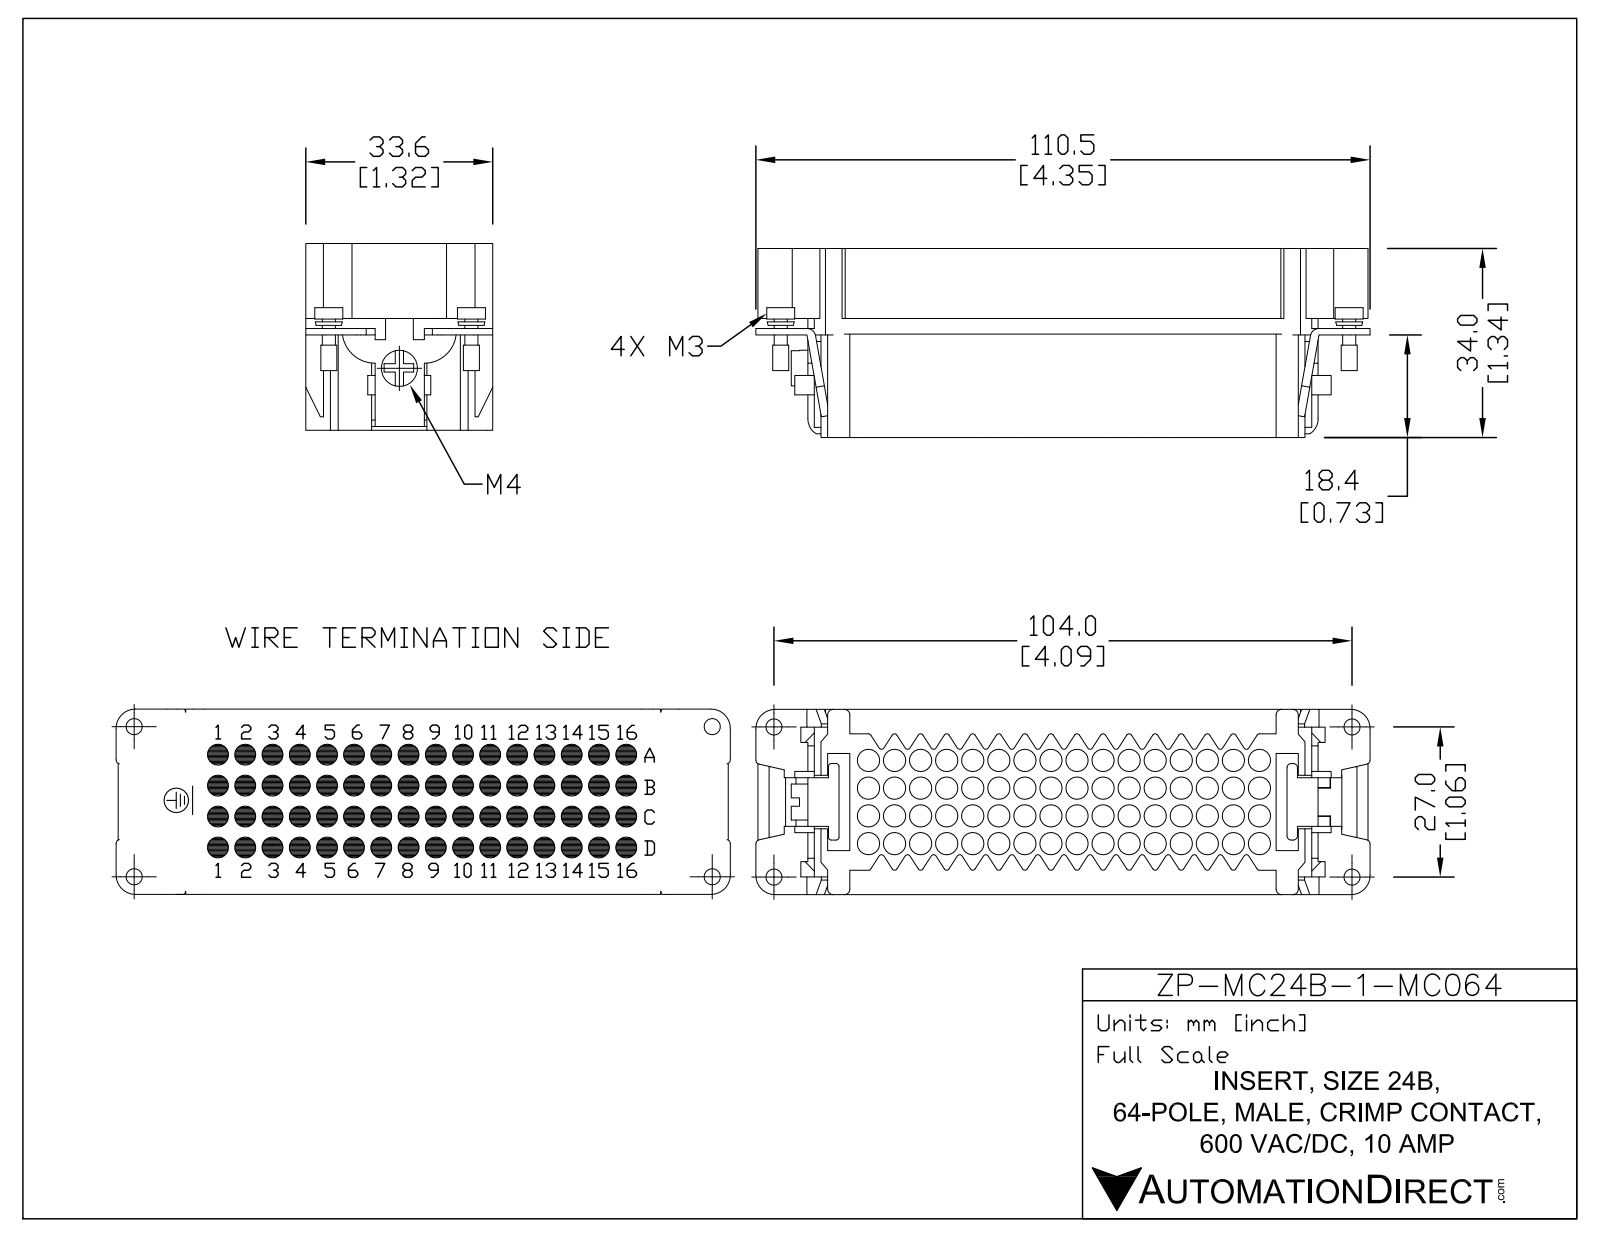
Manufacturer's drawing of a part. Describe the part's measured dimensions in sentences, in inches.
The part is named "ZP-24B-64-MC-INSERT". Its 3-D file was written by "SolidWorks 2011 (AUTOMOTIVE_DESIGN)". It is 2 solids with 613 faces: 377 planar, 232 cylindrical and 4 other. Overall it measures 4.36 by 1.325 by 1.315 inches. Its volume is 2.097 cubic inches and its surface area 67.43 square inches. Round holes: 64 of diameter 0.157, 1 of diameter 0.118. Round bosses or shafts: 32 of diameter 0.187, 4 of diameter 0.199, 4 of diameter 0.114, 4 of diameter 0.093, 1 of diameter 0.256. Partial cylindrical surfaces (rounded edges, fillets, slot ends): 66 of radius 0.02, 16 of radius 0.03, 8 of radius 0.039, 6 of radius 0.059, 4 of radius 0.061, 4 of radius 0.138, 4 of radius 0.258, 2 of radius 0.226. The main face-to-face distances are 0.069, 1.148, 0.156, 0.777, 1.217, 1.079, 0.793, 0.045, 0.048, 0.049. The hole center spacings are 0.185, 0.27, 0.37, 0.419, 0.555, 0.589, 0.74, 0.766.
